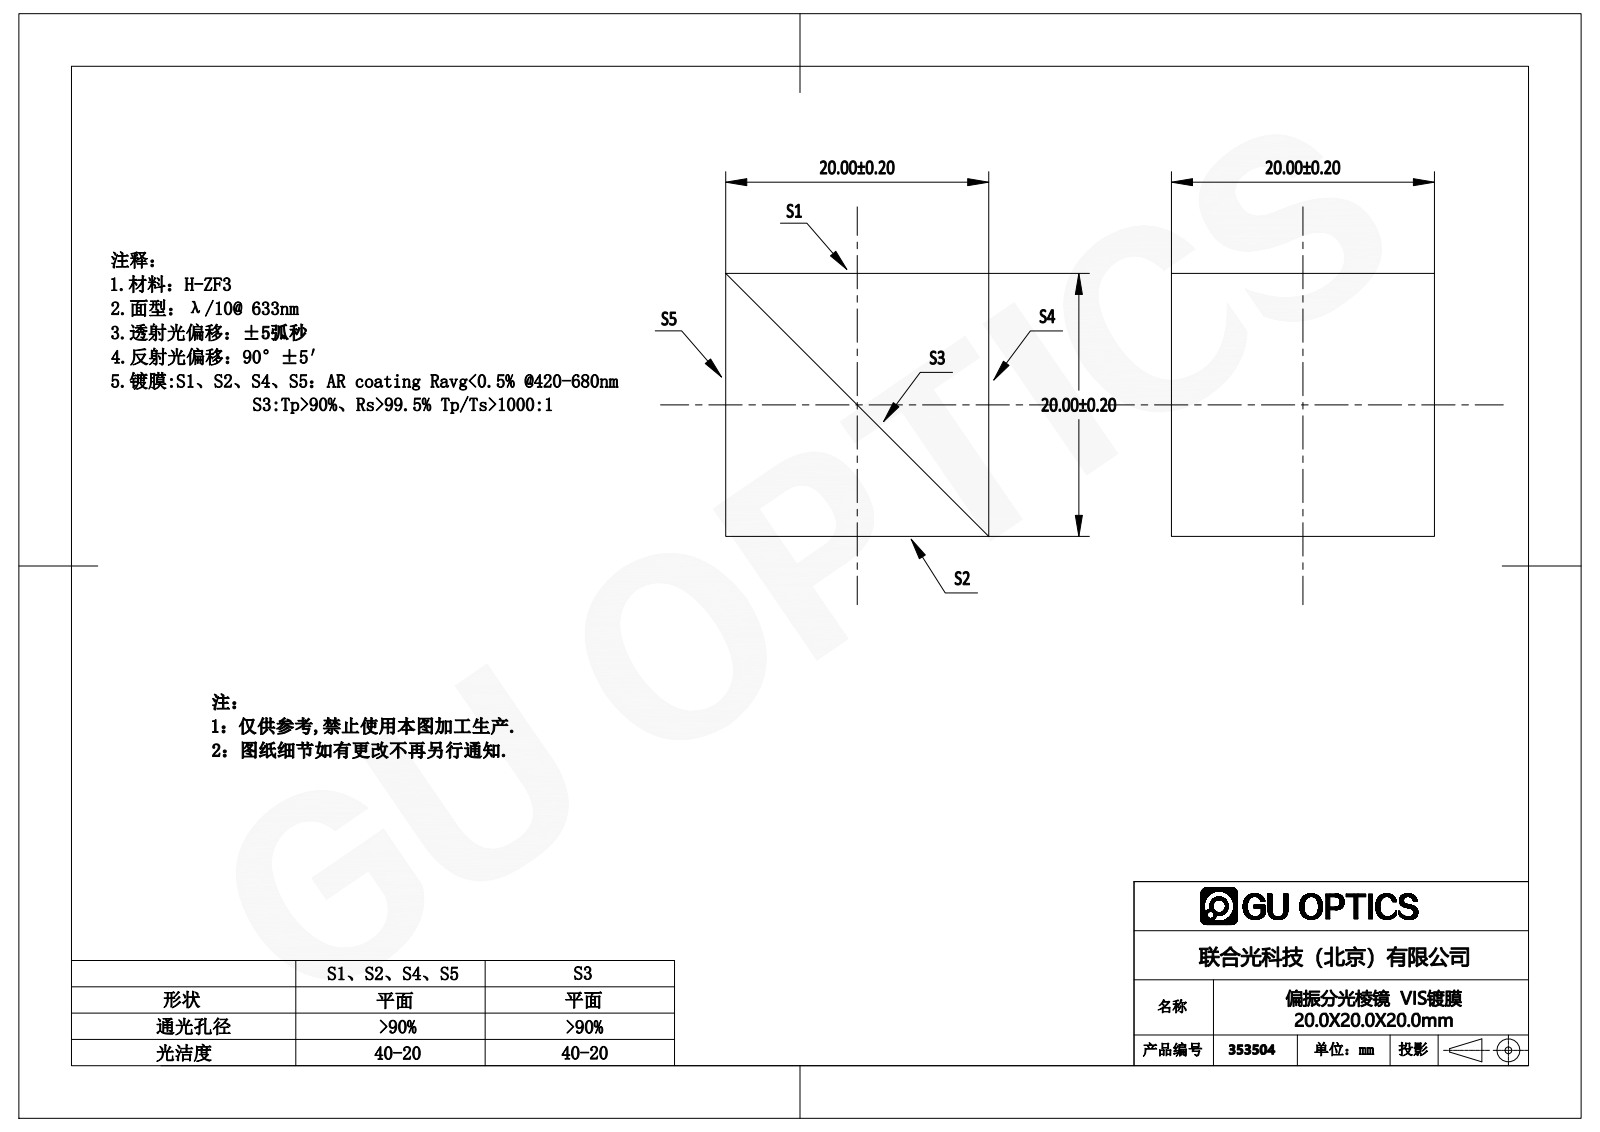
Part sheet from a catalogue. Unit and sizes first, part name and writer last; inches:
Units: inches
Overall size (bounding box): 0.787 × 0.787 × 0.787
Main face-to-face distances: 0.787
Volume: 0.488 in³ · Surface area: 5.473 in²
Bodies: 2 solids, 10 faces (10 planar, 0 cylindrical, 0 other)
Part name (STEP PRODUCT): 352512
STEP written by: SolidWorks 2016 (AUTOMOTIVE_DESIGN)
